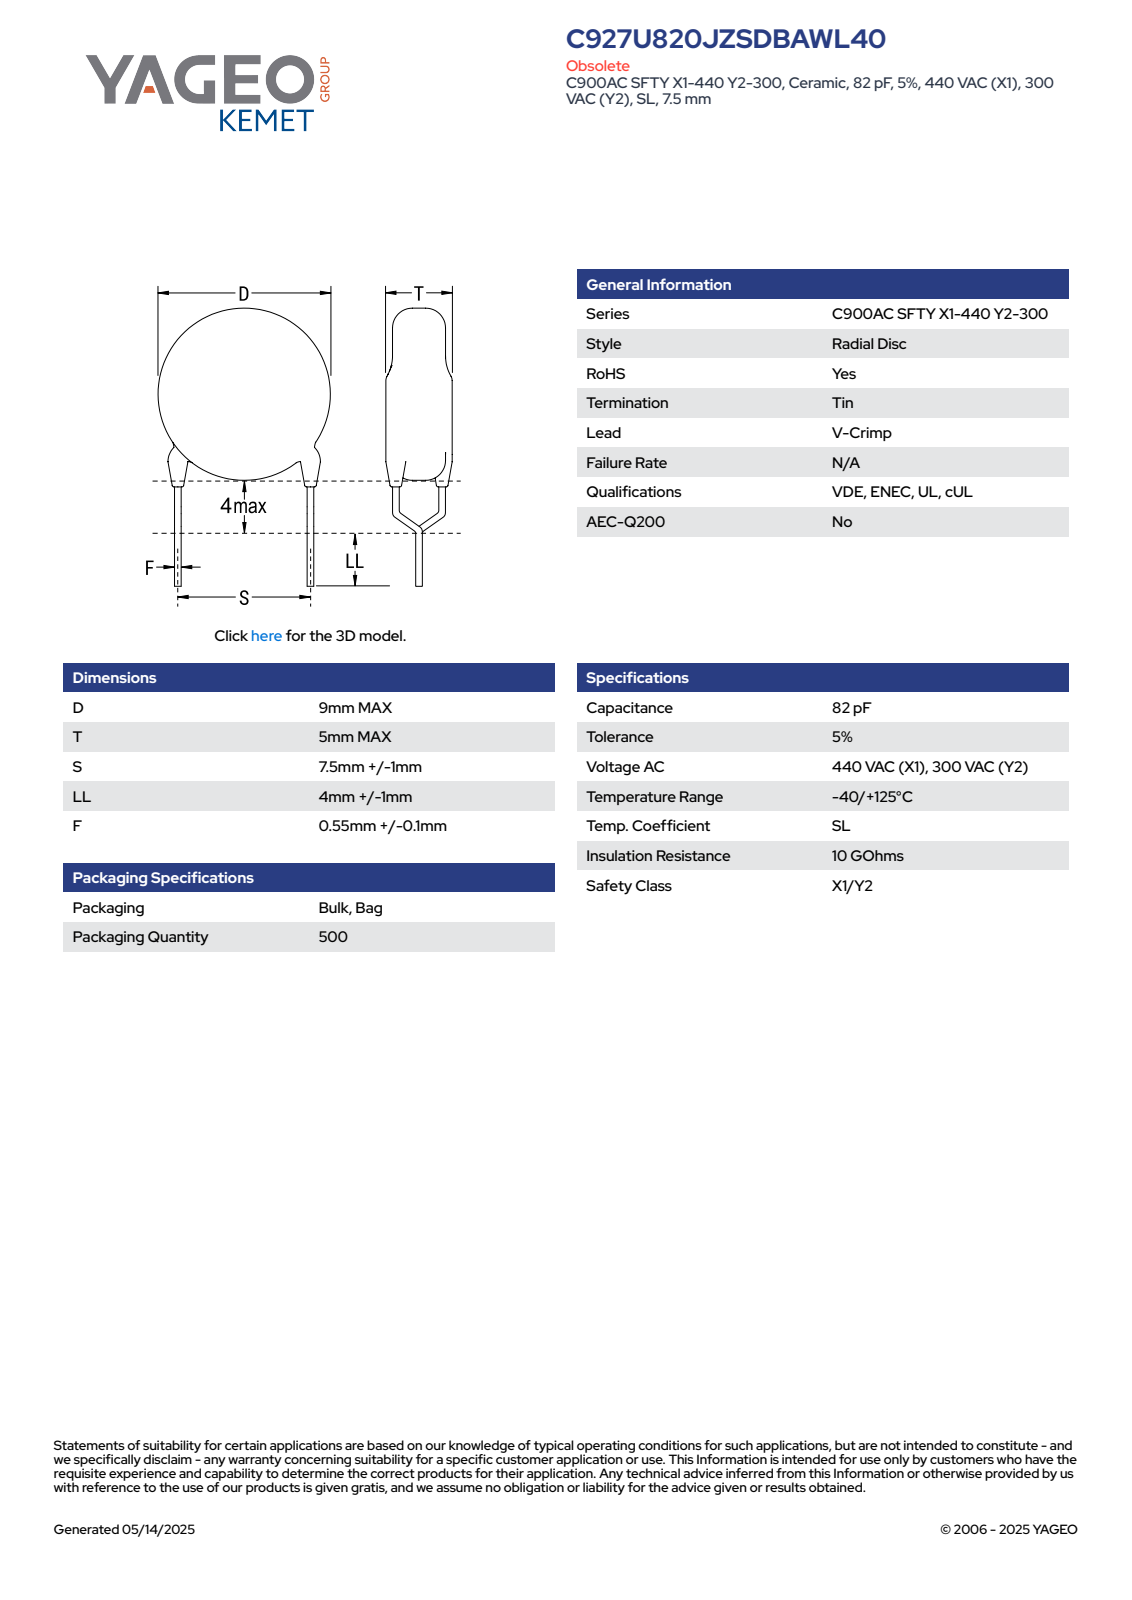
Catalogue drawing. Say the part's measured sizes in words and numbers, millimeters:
The part is named "CCD_VCC900_D9T5S7.5LL5F0.65". Its 3-D file was written by "SolidWorks 2014 (AUTOMOTIVE_DESIGN)". It is 5 solids with 93 faces: 65 planar, 16 cylindrical and 12 other. Overall it measures 17.8 by 9 by 5 millimeters. Its volume is 315 cubic millimeters and its surface area 298 square millimeters. Round bosses or shafts: 6 of diameter 0.65, 1 of diameter 9. The main face-to-face distances are 5, 7.9, 1.17, 13.88, 5.98, 12.71, 4.81, 0.32, 4.77, 3.47.
